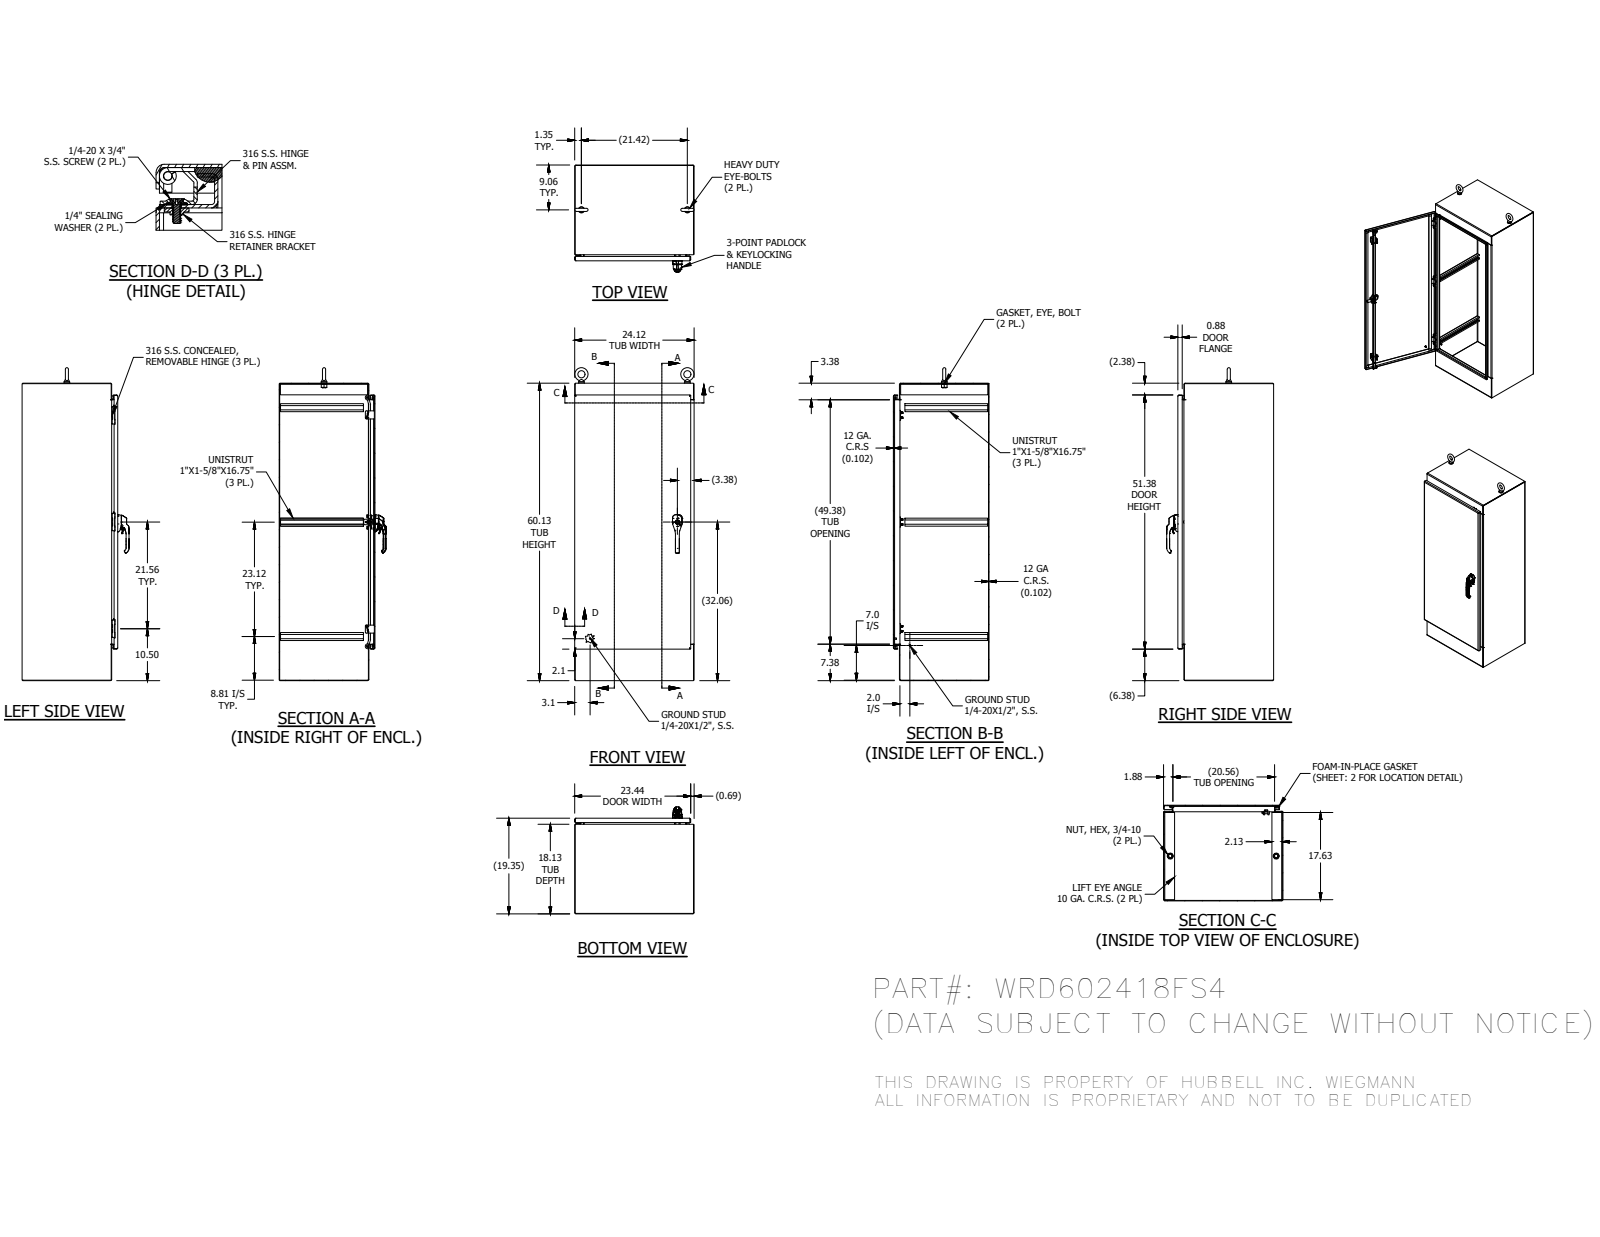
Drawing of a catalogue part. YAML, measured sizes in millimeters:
part_name: "WRD602418FS4BLR; WRD2418FS4TOP; WRD2418FS4BTM; WRD6024FS4DR (+8 more)"
step_written_by: "Autodesk Inventor 2016 (AUTOMOTIVE_DESIGN)"
units: millimeters
bodies: {solids: 76, faces: 3319, planar: 1322, cylindrical: 1133, other: 864}
overall_size: [1606.49, 612.83, 549.04]
volume: 12790000
surface_area: 9593000
round_holes:
  - {diameter: 7.02, count: 8}
  - {diameter: 5.84, count: 6}
  - {diameter: 7.14, count: 6}
  - {diameter: 16.51, count: 6}
  - {diameter: 5.08, count: 4}
  - {diameter: 5.4, count: 3}
  - {diameter: 6, count: 3}
  - {diameter: 7.11, count: 3}
  - {diameter: 6.13, count: 2}
  - {diameter: 6.35, count: 2}
  - {diameter: 6.41, count: 2}
  - {diameter: 10.16, count: 2}
round_bosses_or_shafts:
  - {diameter: 6.35, count: 12}
  - {diameter: 15.88, count: 6}
  - {diameter: 10.25, count: 6}
  - {diameter: 4.63, count: 6}
  - {diameter: 31.75, count: 2}
  - {diameter: 28.45, count: 2}
  - {diameter: 25.4, count: 2}
  - {diameter: 19.05, count: 2}
partial_cylinders:
  - {radius: 0.5, count: 165}
  - {radius: 0.3, count: 84}
  - {radius: 0.25, count: 22}
  - {radius: 1.59, count: 21}
  - {radius: 0.47, count: 19}
  - {radius: 3.17, count: 18}
  - {radius: 2, count: 15}
  - {radius: 1.27, count: 14}
face_to_face_distances: [2.59, 488.83, 610.19, 486.24, 491.42, 607.6, 612.78, 1524.59, 457.79, 31.04]
hole_center_spacings: [12.5, 547.69, 6.5, 22.5, 25.4, 51.5, 512.82, 1090.4]
